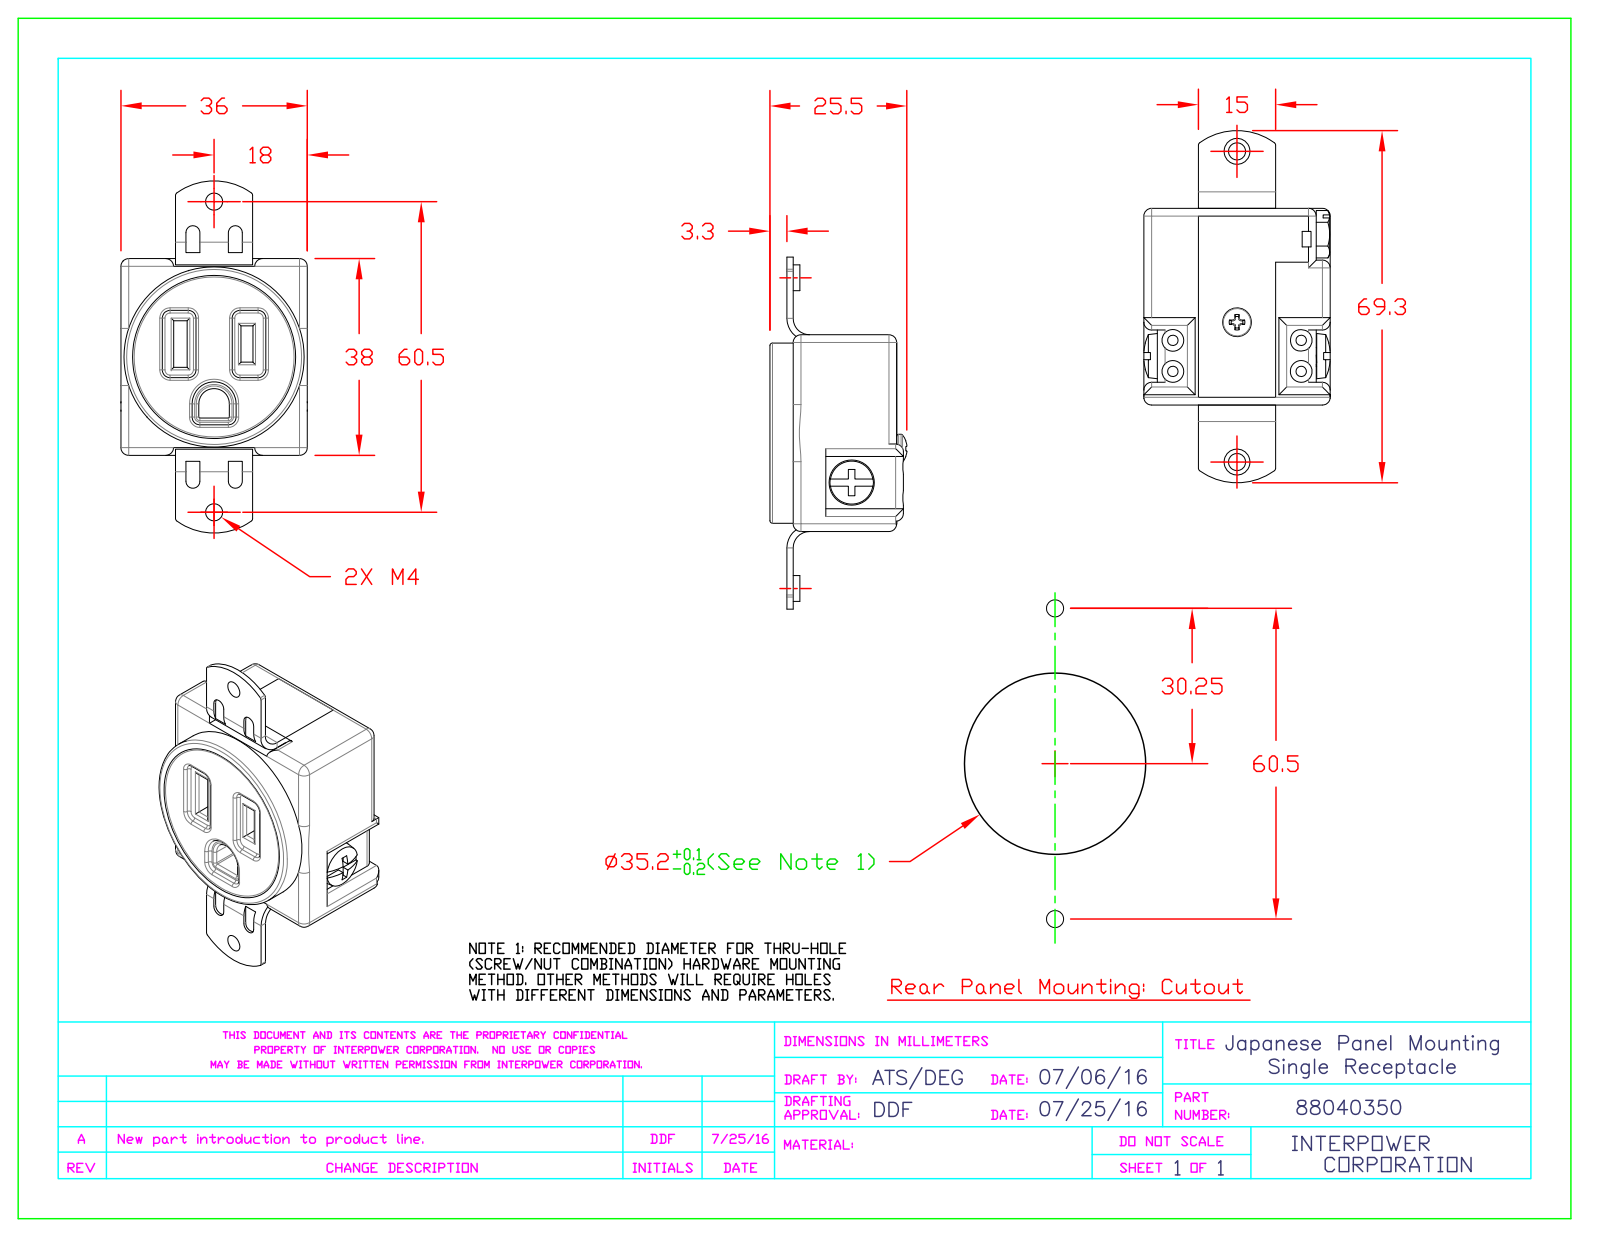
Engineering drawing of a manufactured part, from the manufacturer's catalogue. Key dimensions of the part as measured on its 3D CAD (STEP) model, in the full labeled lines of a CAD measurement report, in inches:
Part name (STEP PRODUCT): 88040350
STEP written by: SolidWorks 2015 (AUTOMOTIVE_DESIGN)
Units: inches
Bodies: 7 solids, 304 faces (127 planar, 123 cylindrical, 54 other)
Overall size (bounding box): 2.677 × 1.417 × 1.016
Volume: 1.82 in³ · Surface area: 17.01 in²
Round holes (diameter × count): ⌀0.079 ×4, ⌀0.165 ×4, ⌀0.13 ×2
Round bosses / shafts (diameter × count): ⌀0.197 ×2, ⌀1.37 ×1
Partial cylindrical surfaces — rounded edges, fillets, slot ends (radius × count): R0.02 ×33, R0.059 ×32, R0.053 ×4, R0.008 ×2, R0.125 ×2, R0.172 ×2, R0.486 ×2, R0.059 ×1
Main face-to-face distances: 0.047, 1.417, 0.787, 0.788, 0.173, 1.496, 0.02, 0.961, 0.961, 1.449
Hole centre spacings: 0.236, 0.844, 0.976, 1.005, 1.046, 1.518, 1.743, 2.362
